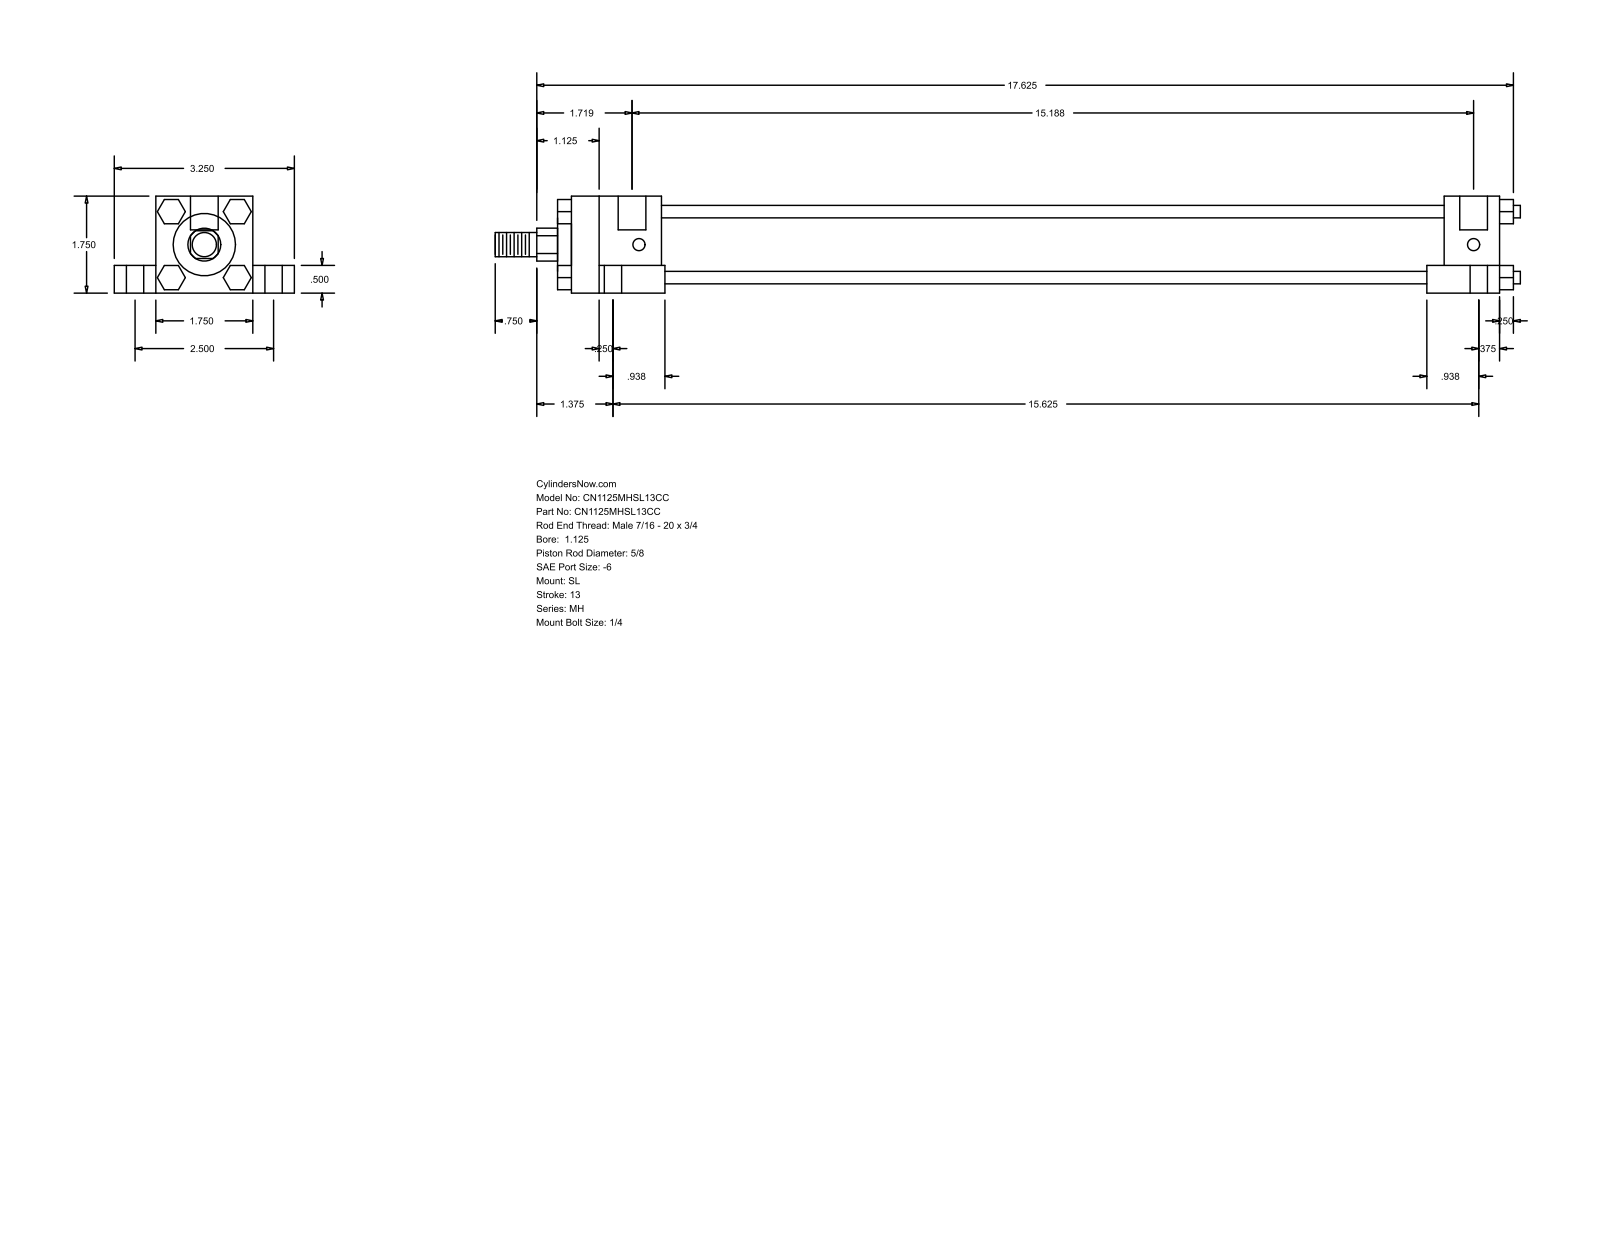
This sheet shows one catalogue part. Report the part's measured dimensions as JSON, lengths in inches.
{"part_name": "MH_SL__0112_0.625", "step_written_by": "GSSL Pune (CONFIG_CONTROL_DESIGN)", "units": "inches", "bodies": {"solids": 0, "faces": 150, "planar": 114, "cylindrical": 36, "other": 0}, "overall_size": [18.5, 3.25, 1.75], "round_holes": [[0.219, 4], [0.313, 4], [0.563, 4], [0.5, 2]], "round_bosses_or_shafts": [[0.225, 4], [1.375, 1], [1.125, 1], [0.625, 1], [0.437, 1]], "partial_cylinders_radius": [[0.297, 1]], "face_to_face_distances": [1.75, 0.75, 0.5, 1.25, 2.5, 0.437, 1.875, 14.125, 15.125, 1], "hole_center_spacings": [1.254, 1.269, 1.296, 2.5, 15.063, 15.208, 15.332, 15.457]}
